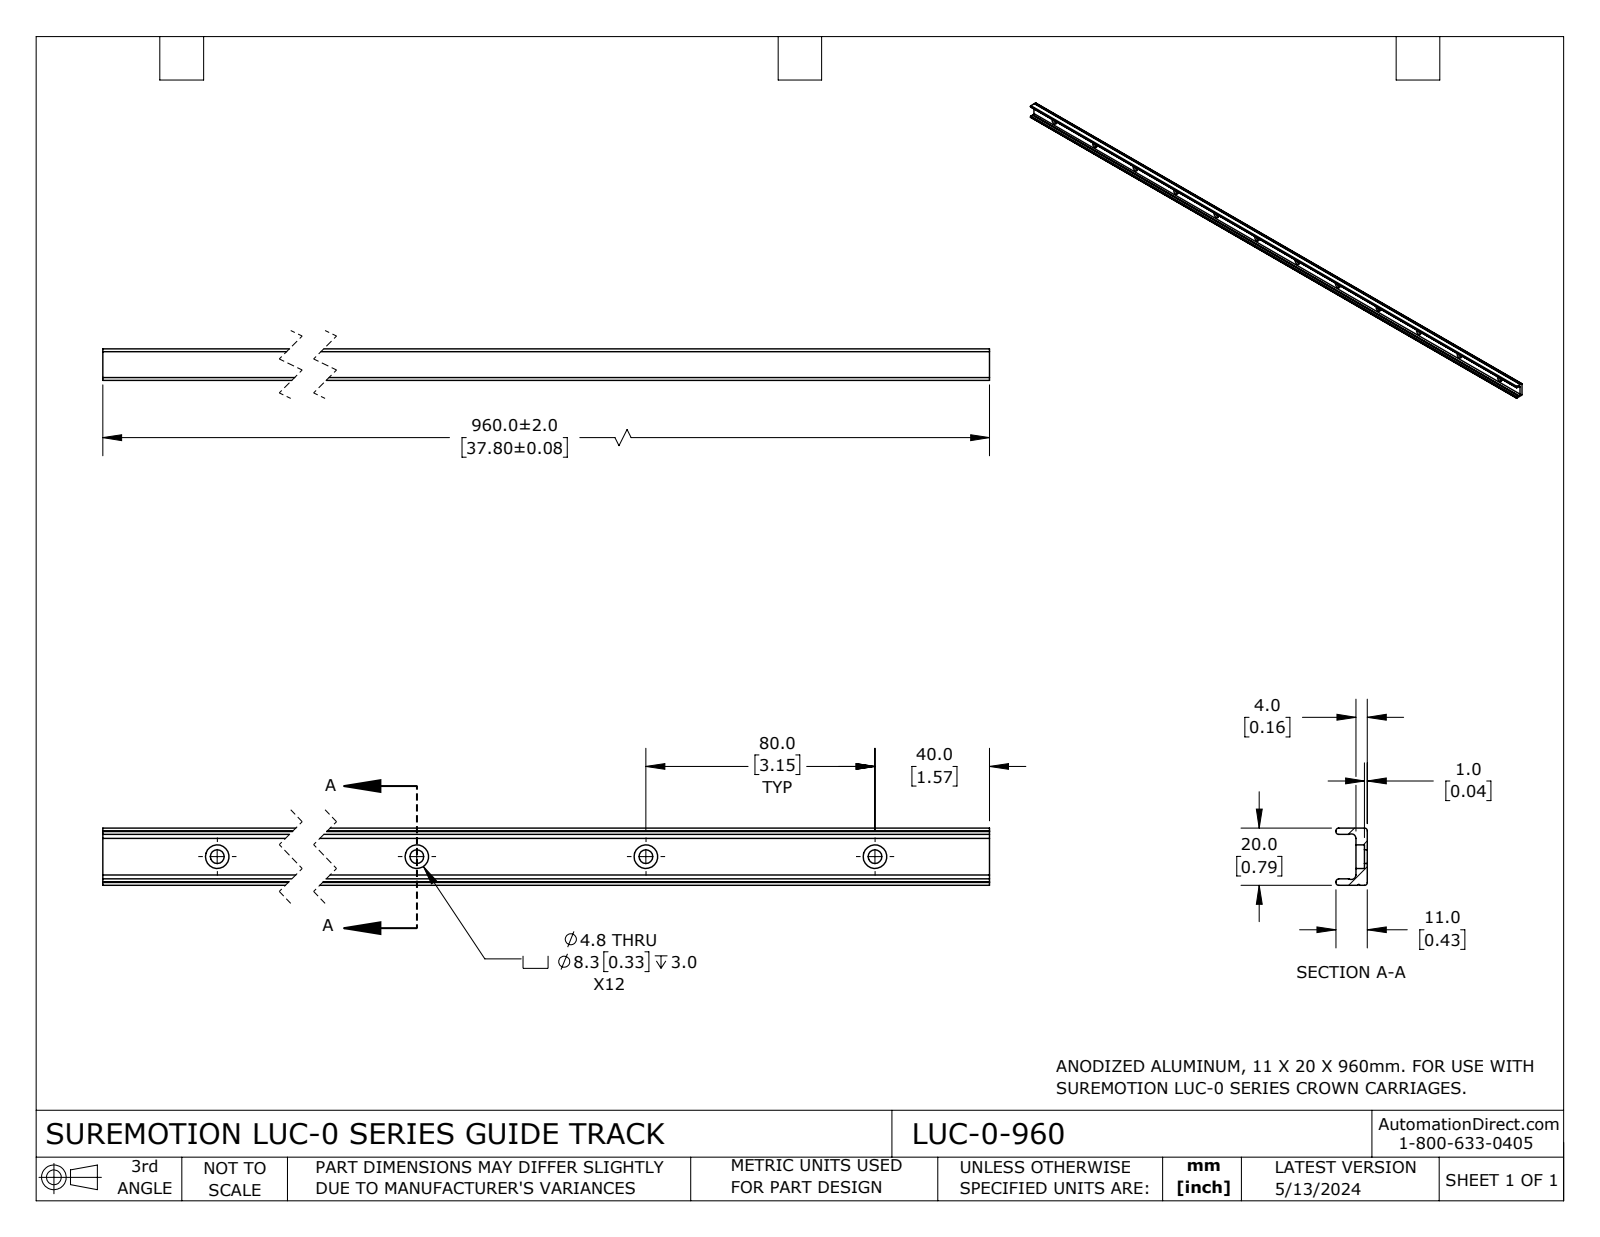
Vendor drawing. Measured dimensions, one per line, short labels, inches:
name: LUC-0-960
written by: SolidWorks 2023 (CONFIG_CONTROL_DESIGN)
unit: in
bodies: 1 solid, 82 faces (23 planar, 59 cylindrical, 0 other)
size: 37.795 × 0.787 × 0.433
volume: 6.319 in³; area: 109.8 in²
holes: 12× ⌀0.189, 7× ⌀0.325, 5× ⌀0.325
rounds: 8× R0.039, 2× R0.063, 1× R0.013
face distances: 0.158, 0.787, 0.088, 0.7, 0.612, 0.433, 0.275, 0.04, 0.118, 0.393
hole spacings: 3.15, 6.299, 9.449, 12.598, 15.748, 18.898, 22.047, 25.197
